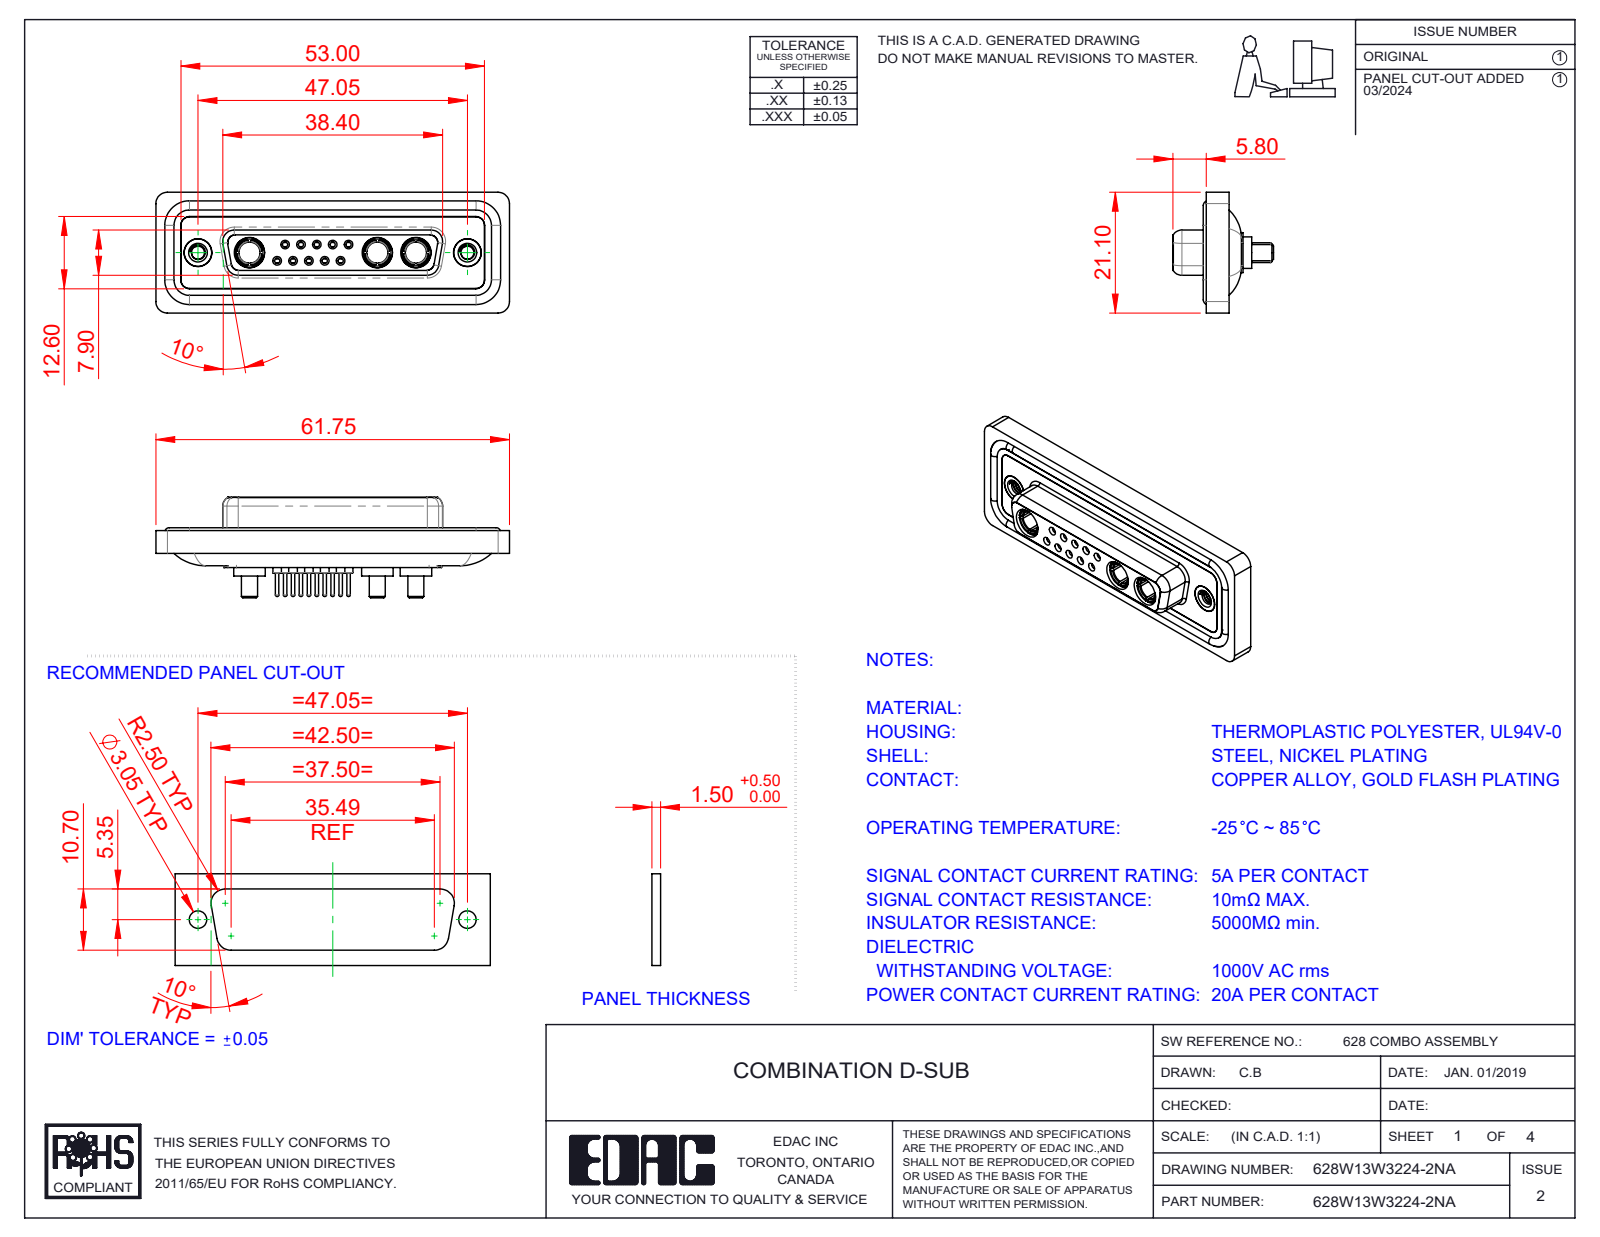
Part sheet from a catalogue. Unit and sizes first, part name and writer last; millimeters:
Units: millimetres
Overall size (bounding box): 61.75 × 21.1 × 17.55
Round holes (diameter × count): ⌀0.9 ×10, ⌀1.1 ×10, ⌀1.5 ×10, ⌀2 ×10, ⌀1.6 ×5, ⌀1.7 ×5, ⌀4.85 ×5, ⌀3.7 ×3, ⌀5.3 ×3, ⌀2.26 ×2, ⌀4 ×2, ⌀4.05 ×2
Round bosses / shafts (diameter × count): ⌀2.2 ×10, ⌀0.6 ×10, ⌀1.6 ×9, ⌀5.5 ×3, ⌀5.2 ×3, ⌀4.96 ×3, ⌀4.75 ×3, ⌀3.75 ×3
Partial cylindrical surfaces — rounded edges, fillets, slot ends (radius × count): R1.5 ×22, R2 ×18, R1.35 ×8, R1.6 ×8, R0.25 ×4, R0.5 ×4, R0.6 ×4, R0.65 ×4
Main face-to-face distances: 0.4, 1.8, 7.45, 5.65, 0.5, 6.6, 7.05, 1.6, 2.9, 1.1
Hole centre spacings: 3.16, 2.77, 5.03, 5.04, 5.54, 8.31, 7.49, 2.76
Volume: 8 275 mm³ · Surface area: 13 706 mm²
Bodies: 23 solids, 1156 faces (342 planar, 449 cylindrical, 365 other)
Part name (STEP PRODUCT): 628Combo Contact Row 1_24; 628W13W3224-2NA; 628Combo Waterproof Housing_25 Contacts; 628Combo Contact Row 2_24 (+5 more)
STEP written by: SolidWorks 2023 (CONFIG_CONTROL_DESIGN)
